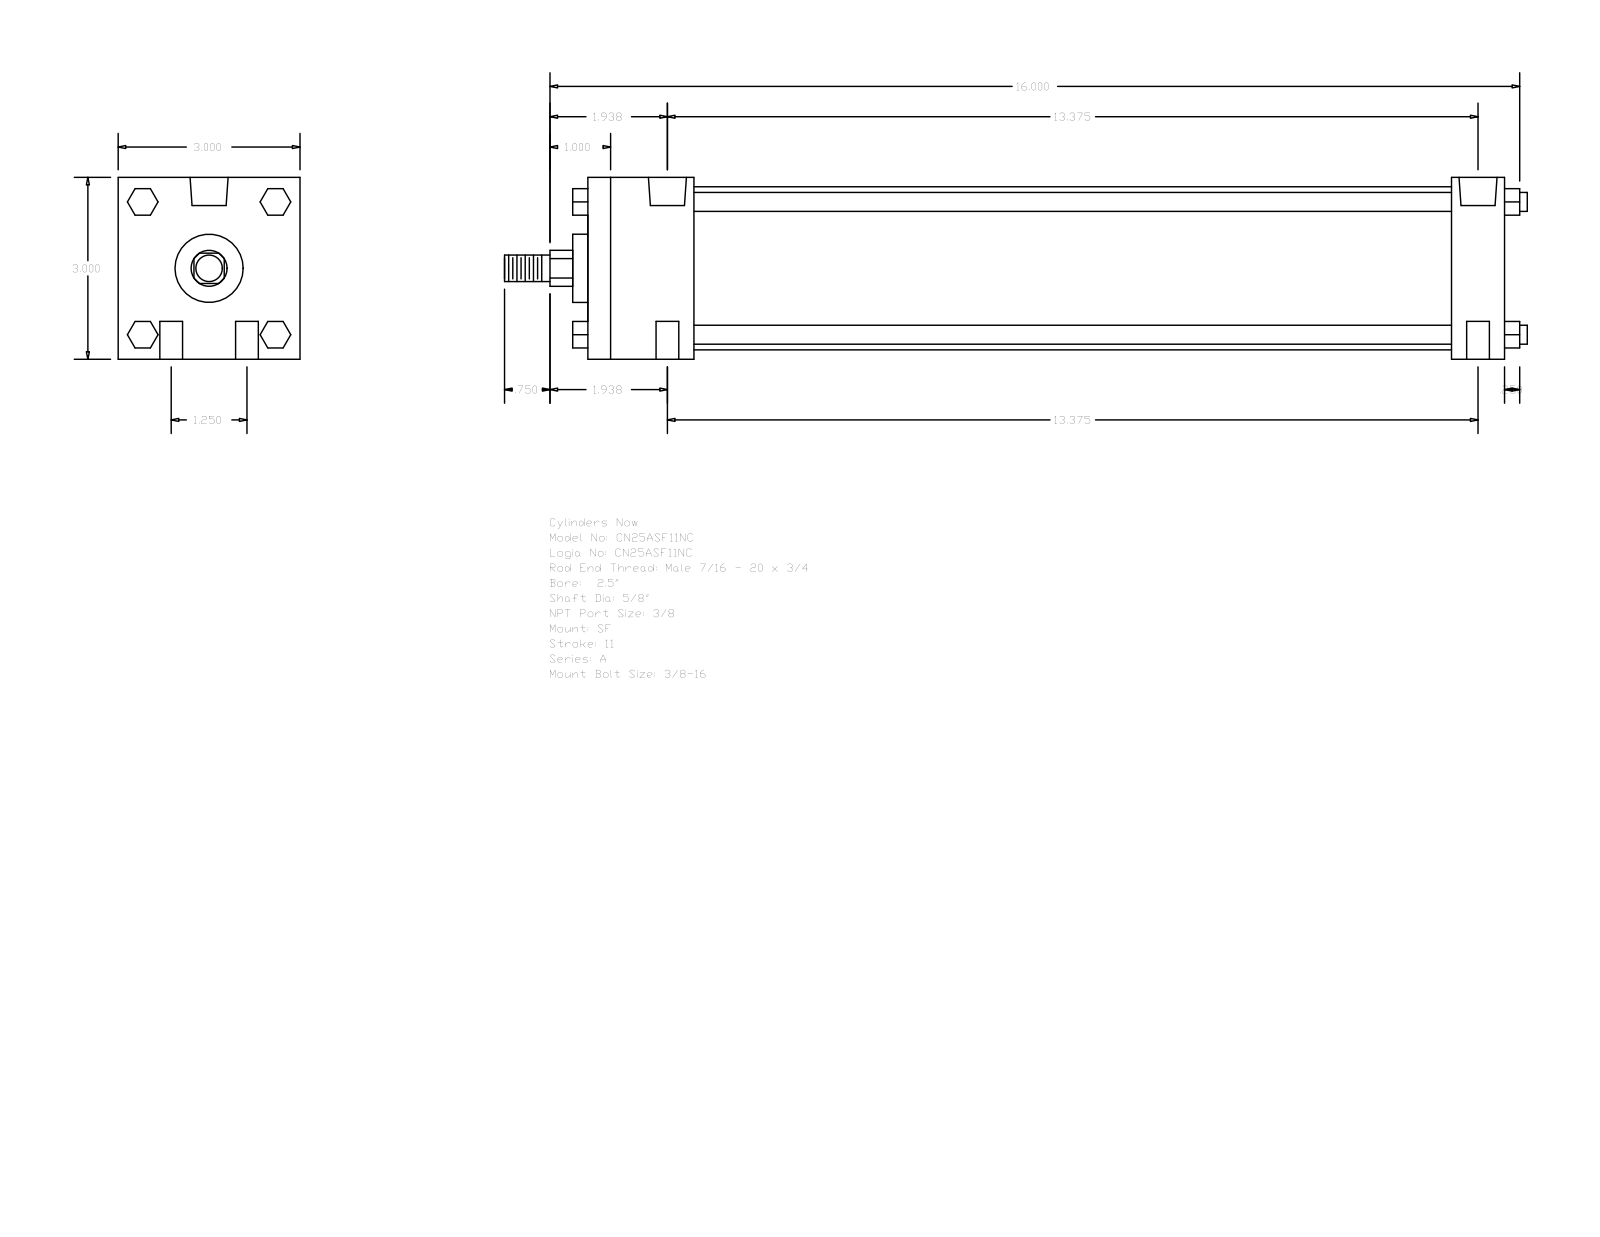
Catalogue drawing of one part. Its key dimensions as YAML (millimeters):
part_name: "A_SF__0250_0.625"
step_written_by: "GSSL Pune (CONFIG_CONTROL_DESIGN)"
units: millimeters
bodies: {solids: 0, faces: 124, planar: 94, cylindrical: 30, other: 0}
overall_size: [428.62, 76.2, 76.2]
round_holes:
  - {diameter: 9.53, count: 4}
  - {diameter: 5.56, count: 2}
  - {diameter: 15.93, count: 2}
round_bosses_or_shafts:
  - {diameter: 7.94, count: 4}
  - {diameter: 68.33, count: 1}
  - {diameter: 28.57, count: 1}
  - {diameter: 15.88, count: 1}
  - {diameter: 11.11, count: 1}
partial_cylinders:
  - {radius: 7.54, count: 1}
face_to_face_distances: [76.2, 384.17, 44.45, 361.94, 22.23, 317.49, 339.72, 6.35, 390.52, 50.8]
hole_center_spacings: [15.88, 340.1, 339.73, 31.76, 341.21, 344.49]
